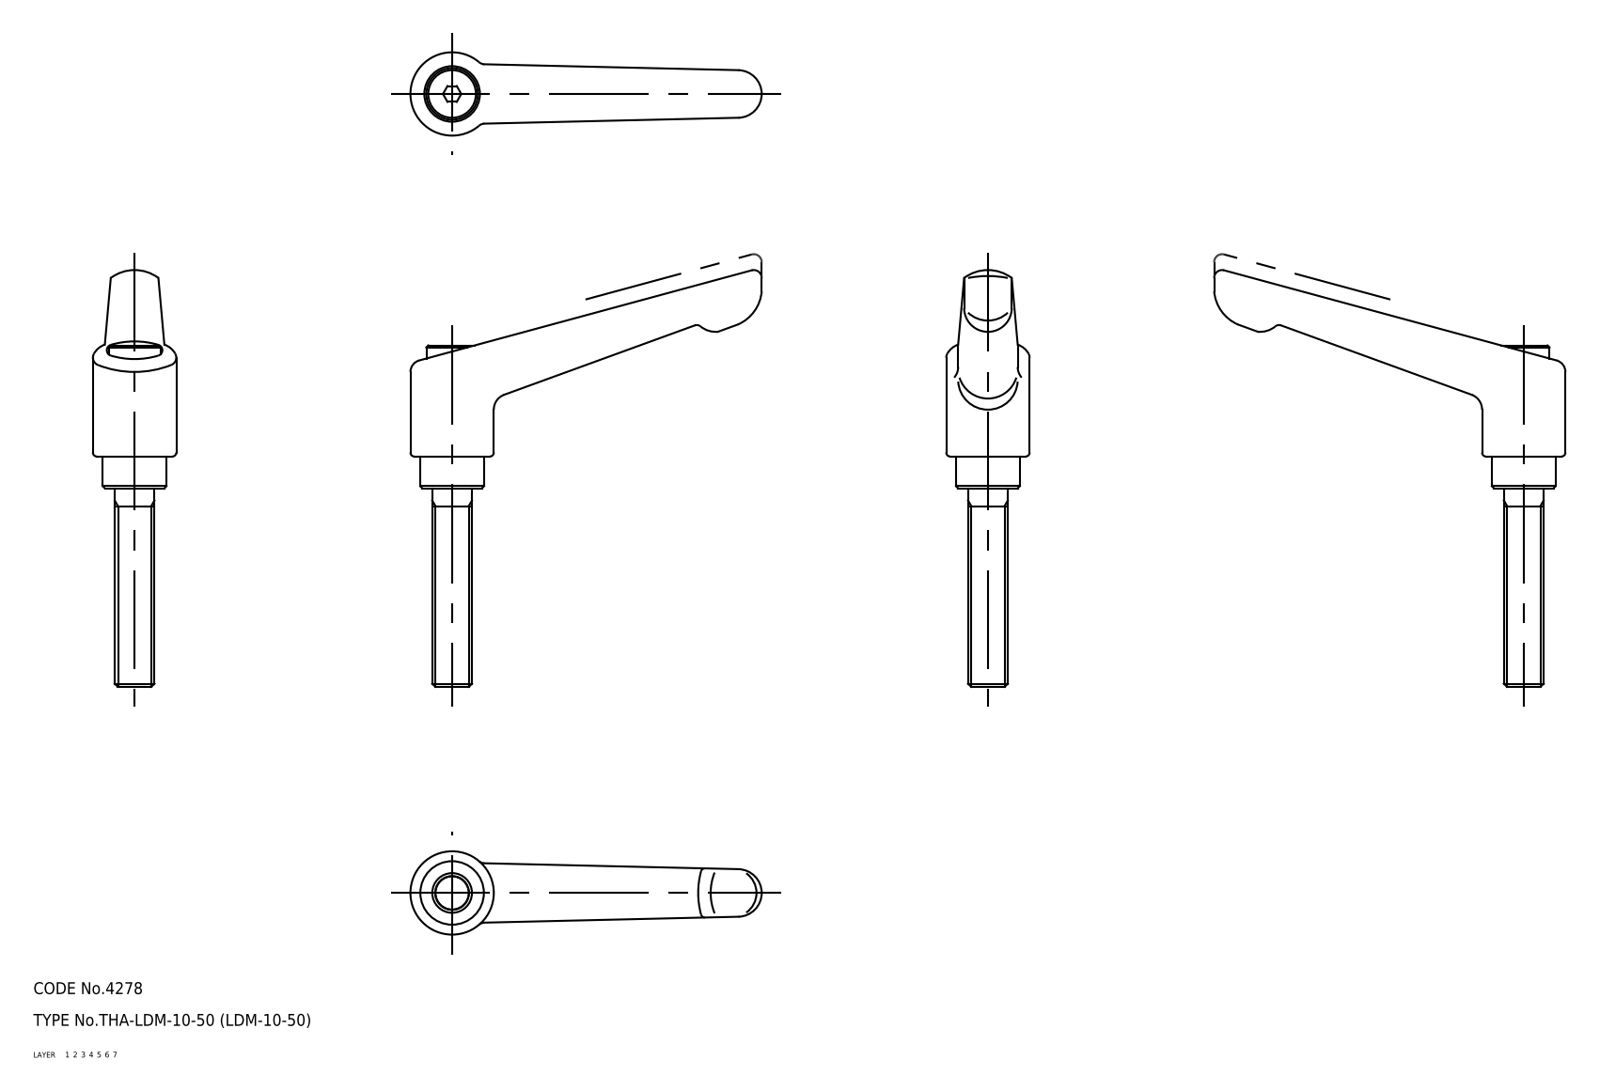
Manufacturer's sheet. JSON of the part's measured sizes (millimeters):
{"part_name": "sleeve; screw; handle; LDM_10_50_26123_36", "step_written_by": "CADfix (AUTOMOTIVE_DESIGN)", "units": "millimeters", "bodies": {"solids": 3, "faces": 75, "planar": 0, "cylindrical": 0, "other": 75}, "overall_size": [105, 88.5, 21], "volume_mm3": 23289, "surface_area_mm2": 9901}
